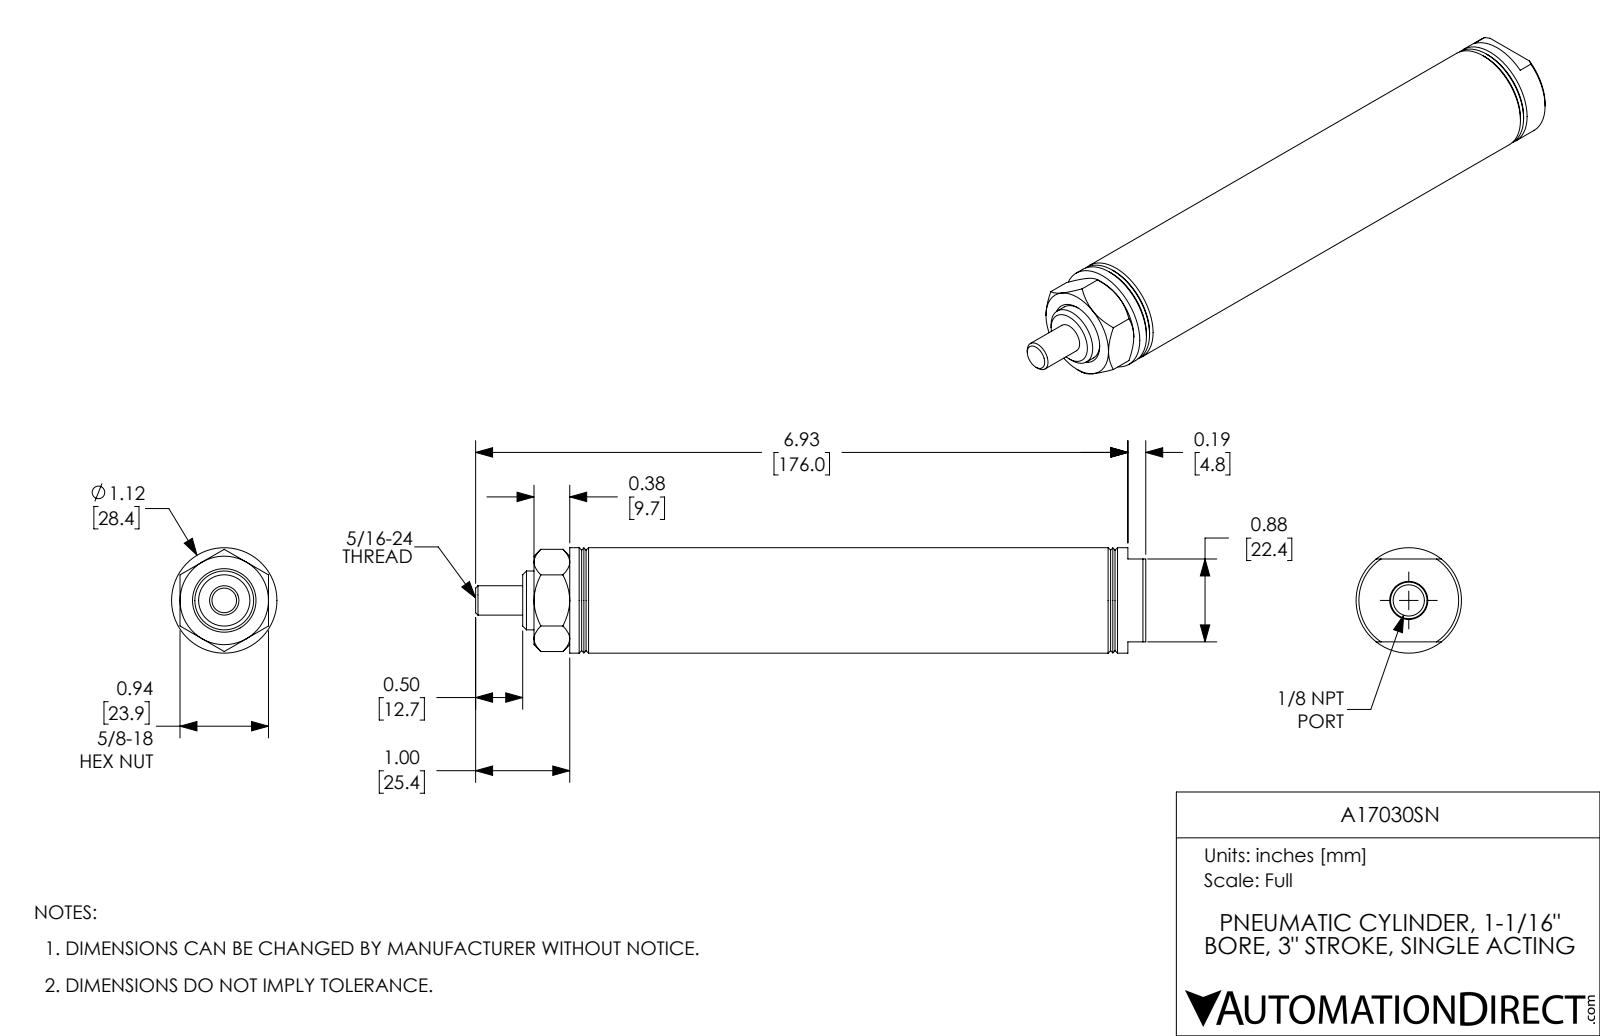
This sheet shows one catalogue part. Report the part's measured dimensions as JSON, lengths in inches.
{"part_name": "A17030SN; A17030SN-Rod; A17030SN_Mounting Nut_D-9; A17030SN-MainBody", "step_written_by": "SolidWorks 2017 (AUTOMOTIVE_DESIGN)", "units": "inches", "bodies": {"solids": 3, "faces": 82, "planar": 21, "cylindrical": 20, "other": 41}, "overall_size": [7.12, 1.12, 1.12], "volume_in3": 3.803, "surface_area_in2": 52.33, "round_holes": [[0.312, 1], [0.332, 1], [0.625, 1], [1.063, 1]], "round_bosses_or_shafts": [[1.12, 1]], "face_to_face_distances": [4.81, 0.5, 3.5, 1.31, 3, 4.31, 1.31, 1.81, 4.81, 6.12]}
